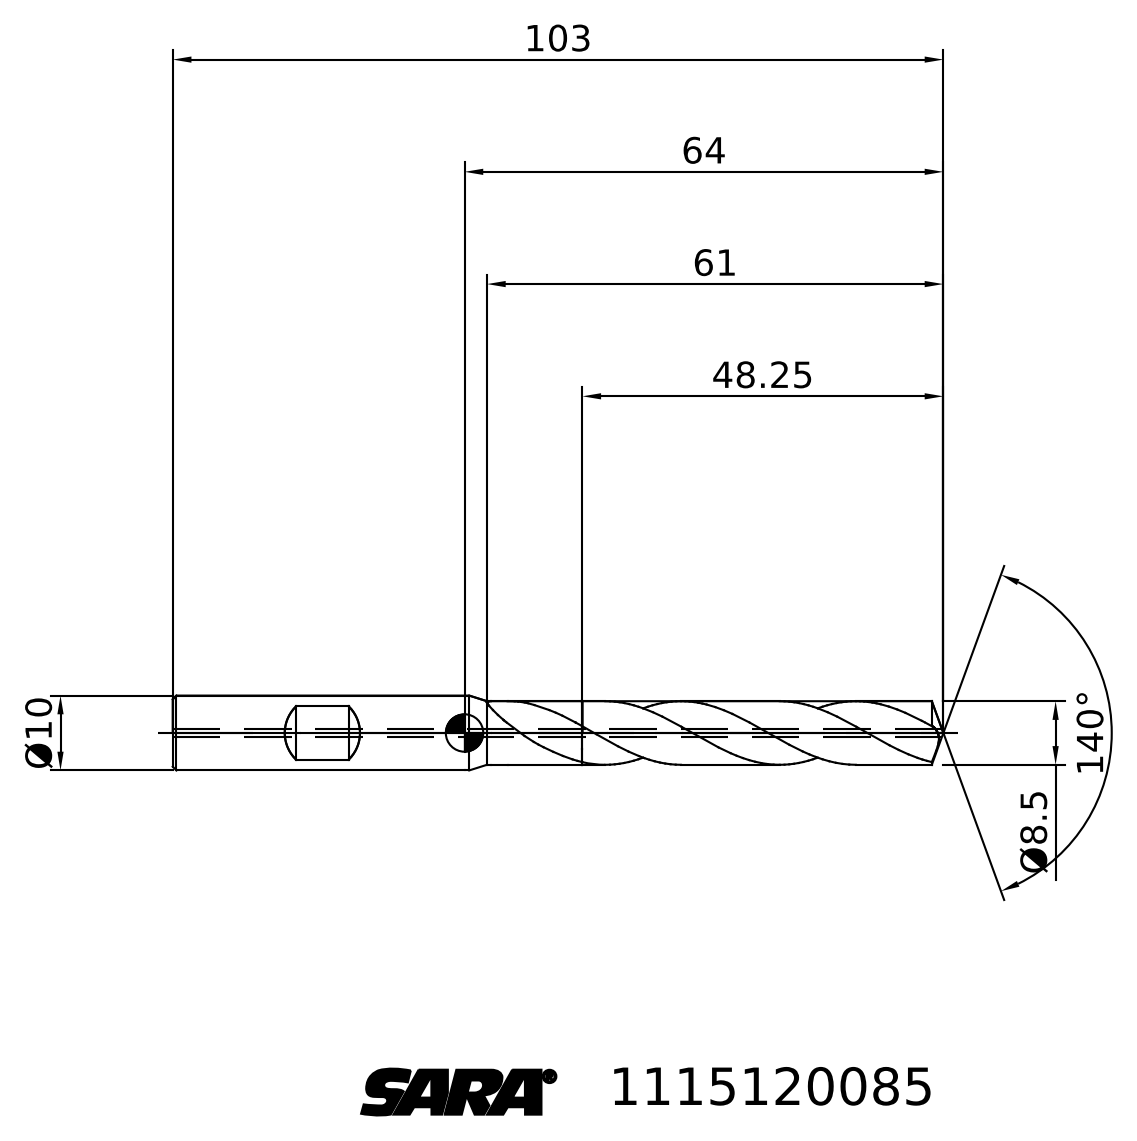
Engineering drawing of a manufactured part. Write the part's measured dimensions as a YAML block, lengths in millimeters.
step_written_by: "TDM (AUTOMOTIVE_DESIGN)"
units: millimeters
bodies: {solids: 2, faces: 31, planar: 6, cylindrical: 0, other: 25}
overall_size: [103, 10.26, 10]
volume: 5489
surface_area: 3242
face_to_face_distances: [54.75]
